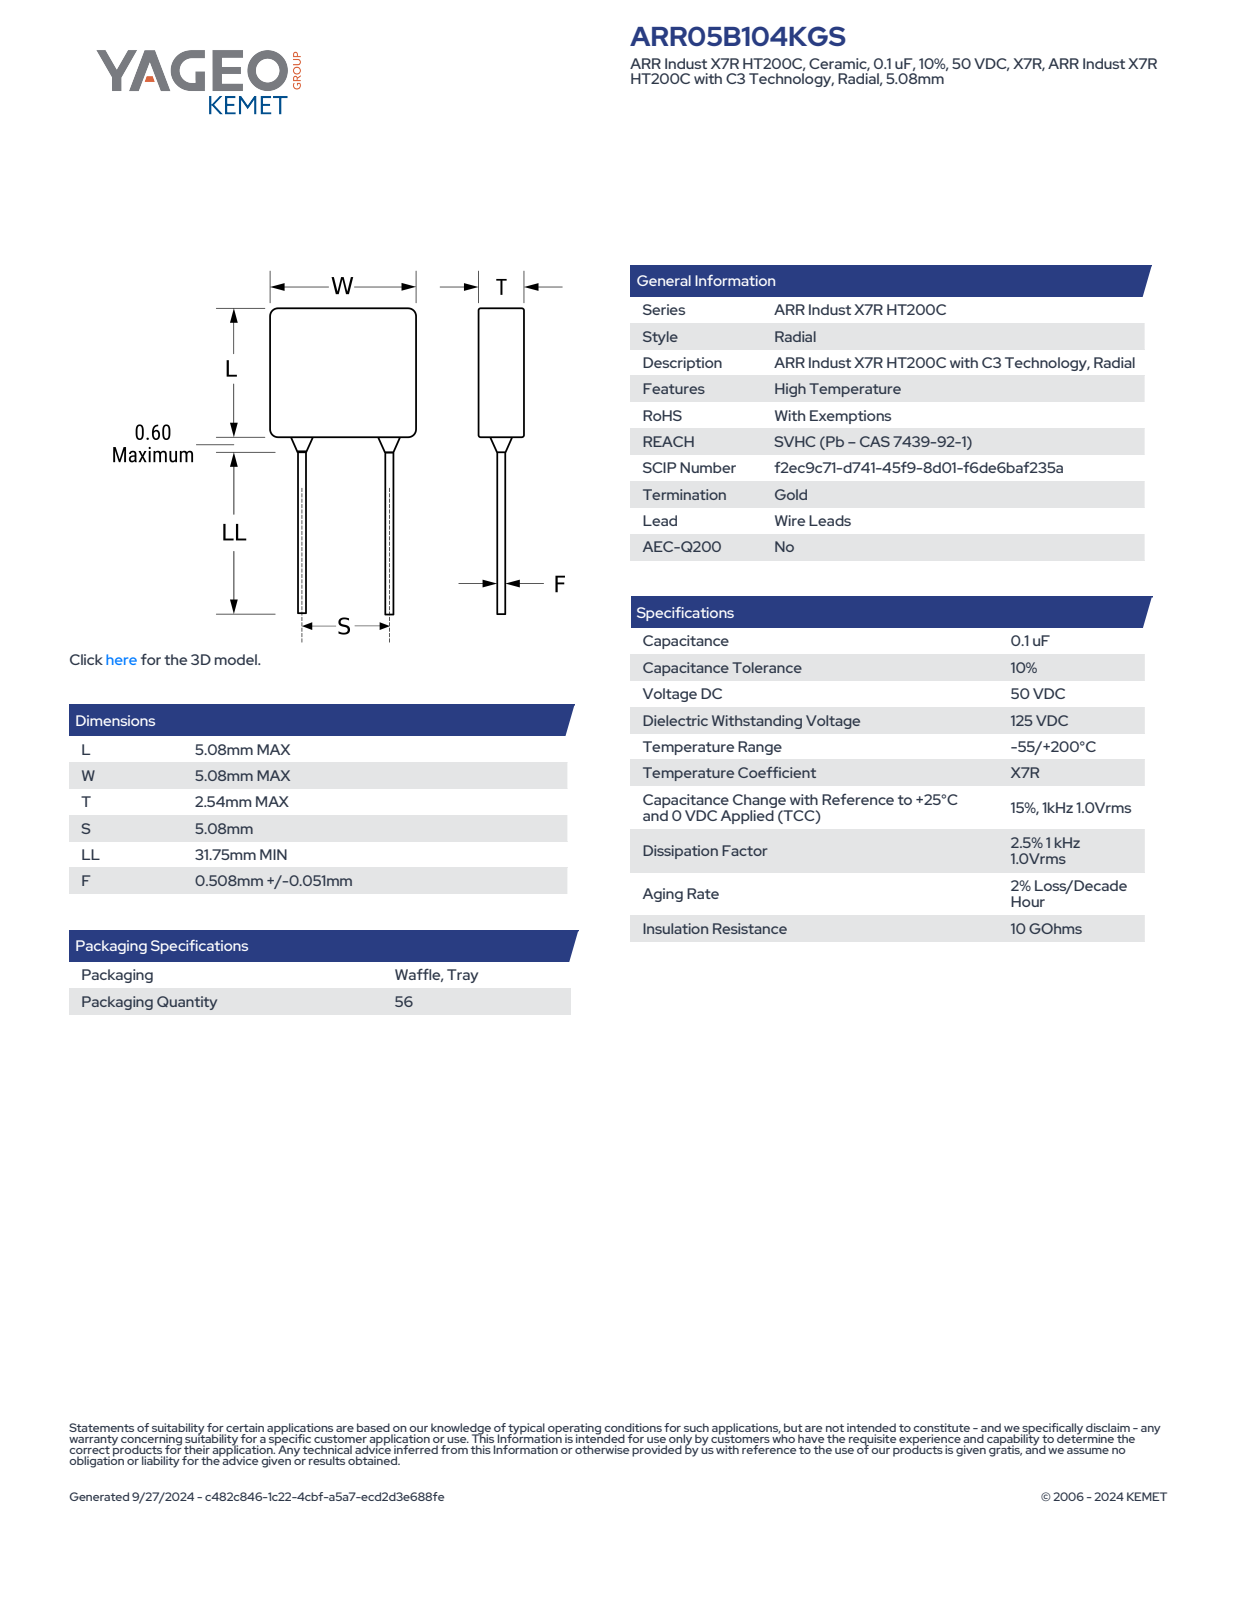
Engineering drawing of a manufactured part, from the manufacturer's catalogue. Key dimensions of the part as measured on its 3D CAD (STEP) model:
Part name (STEP PRODUCT): CCR_C3_5_L5.08T2.54S5.842LL3.175F0.559W5.08
STEP written by: SolidWorks 2021 (AUTOMOTIVE_DESIGN)
Units: millimetres
Bodies: 4 solids, 77 faces (65 planar, 8 cylindrical, 4 other)
Overall size (bounding box): 8.49 × 5.08 × 2.54
Volume: 67 mm³ · Surface area: 118 mm²
Round bosses / shafts (diameter × count): ⌀0.56 ×2
Partial cylindrical surfaces — rounded edges, fillets, slot ends (radius × count): R0.2 ×4
Main face-to-face distances: 2.54, 5.08, 3.41, 8.49, 6.28, 2.87, 2.21, 5.51, 2.1, 0.77
